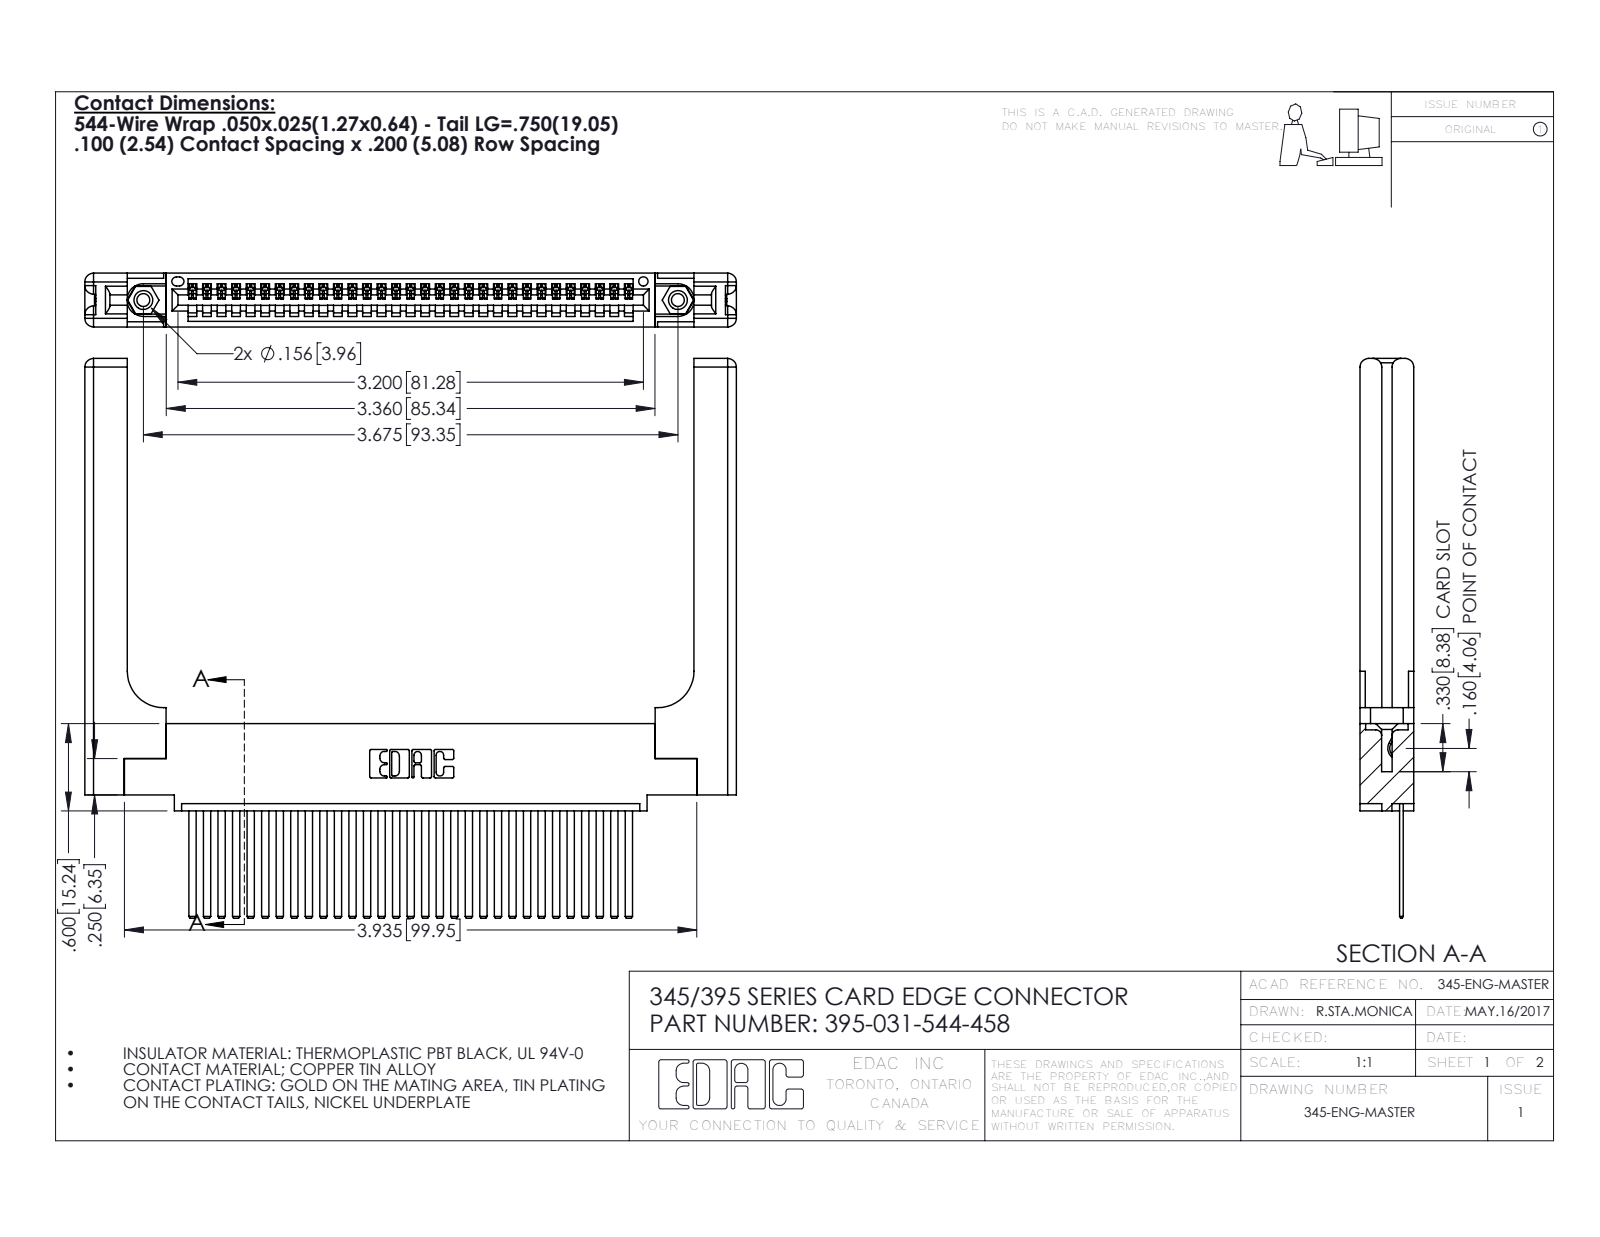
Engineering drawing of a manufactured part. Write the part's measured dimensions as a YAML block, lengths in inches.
part_name: "395-031-544-458; 345-292-001_345-293-144; 345-250-001_345-250-001-102; 345 Part_0.110 Offset - 0.156 Dia-TH (+1 more)"
step_written_by: "SolidWorks 2016 (CONFIG_CONTROL_DESIGN)"
units: inches
bodies: {solids: 36, faces: 1998, planar: 1348, cylindrical: 590, other: 60}
overall_size: [4.479, 3.847, 0.37]
volume: 1.19
surface_area: 32.45
round_holes:
  - {diameter: 0.089, count: 2}
  - {diameter: 0.125, count: 2}
  - {diameter: 0.156, count: 2}
  - {diameter: 0.064, count: 1}
round_bosses_or_shafts:
  - {diameter: 0.155, count: 2}
partial_cylinders:
  - {radius: 0.006, count: 62}
  - {radius: 0.01, count: 22}
  - {radius: 0.06, count: 16}
  - {radius: 0.007, count: 6}
  - {radius: 0.031, count: 6}
  - {radius: 0.026, count: 3}
  - {radius: 0.03, count: 2}
  - {radius: 0.031, count: 2}
face_to_face_distances: [0.072, 0.298, 0.37, 0.098, 0.272, 0.025, 0.2, 0.148, 0.15, 0.077]
hole_center_spacings: [0.27, 3.44, 3.675]
